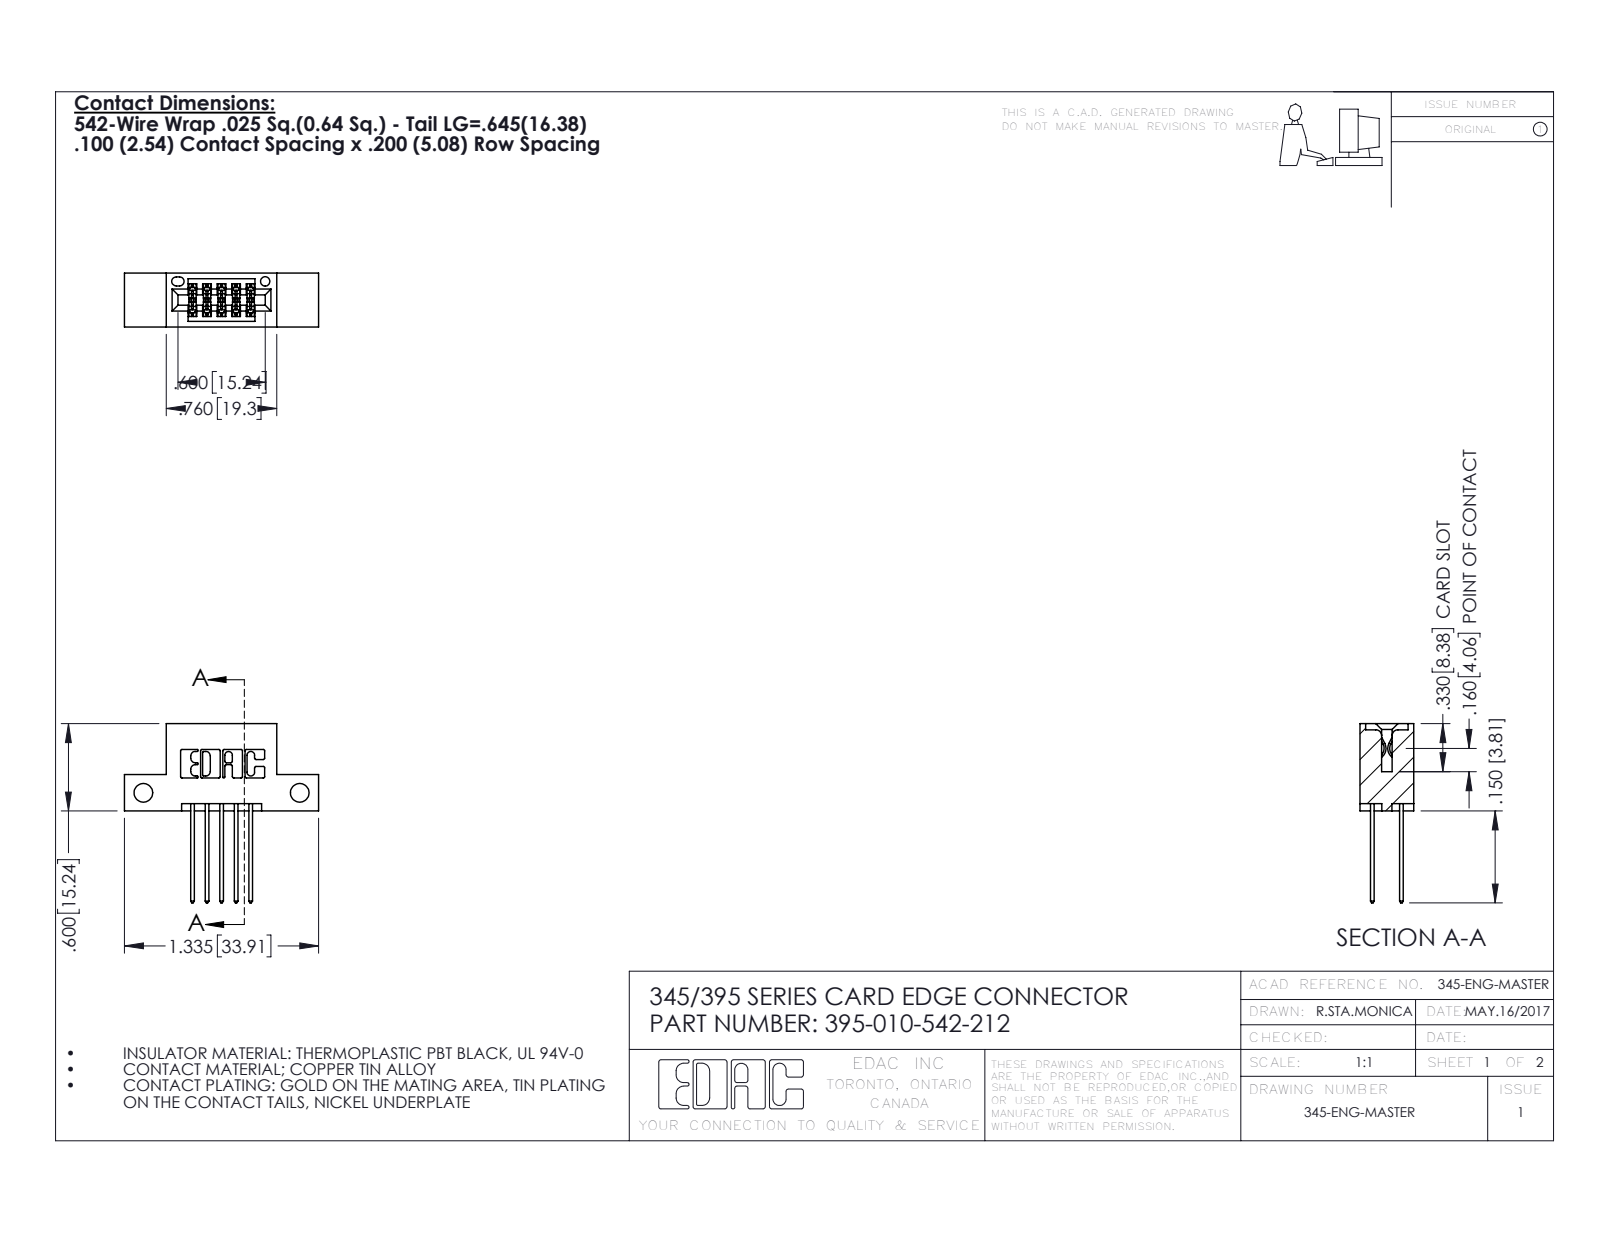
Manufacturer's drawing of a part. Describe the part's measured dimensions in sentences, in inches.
The part is named "345-292-001_345-293-142; 395-010-542-212; 345 Part_Flush Mounting Lugs - Side Mount". Its 3-D file was written by "SolidWorks 2016 (CONFIG_CONTROL_DESIGN)". It is 11 solids with 626 faces: 410 planar, 216 cylindrical and 0 other. Overall it measures 1.335 by 1.232 by 0.37 inches. Its volume is 0.178 cubic inches and its surface area 5.684 square inches. Round holes: 2 of diameter 0.128, 1 of diameter 0.064. Partial cylindrical surfaces (rounded edges, fillets, slot ends): 22 of radius 0.01, 15 of radius 0.006, 10 of radius 0.01, 6 of radius 0.007, 6 of radius 0.031, 3 of radius 0.026, 2 of radius 0.014, 2 of radius 0.019. The main face-to-face distances are 0.2, 0.298, 0.072, 0.1, 0.37, 0.098, 0.272, 0.025, 0.25, 0.225. The hole center spacings are 1.075.
